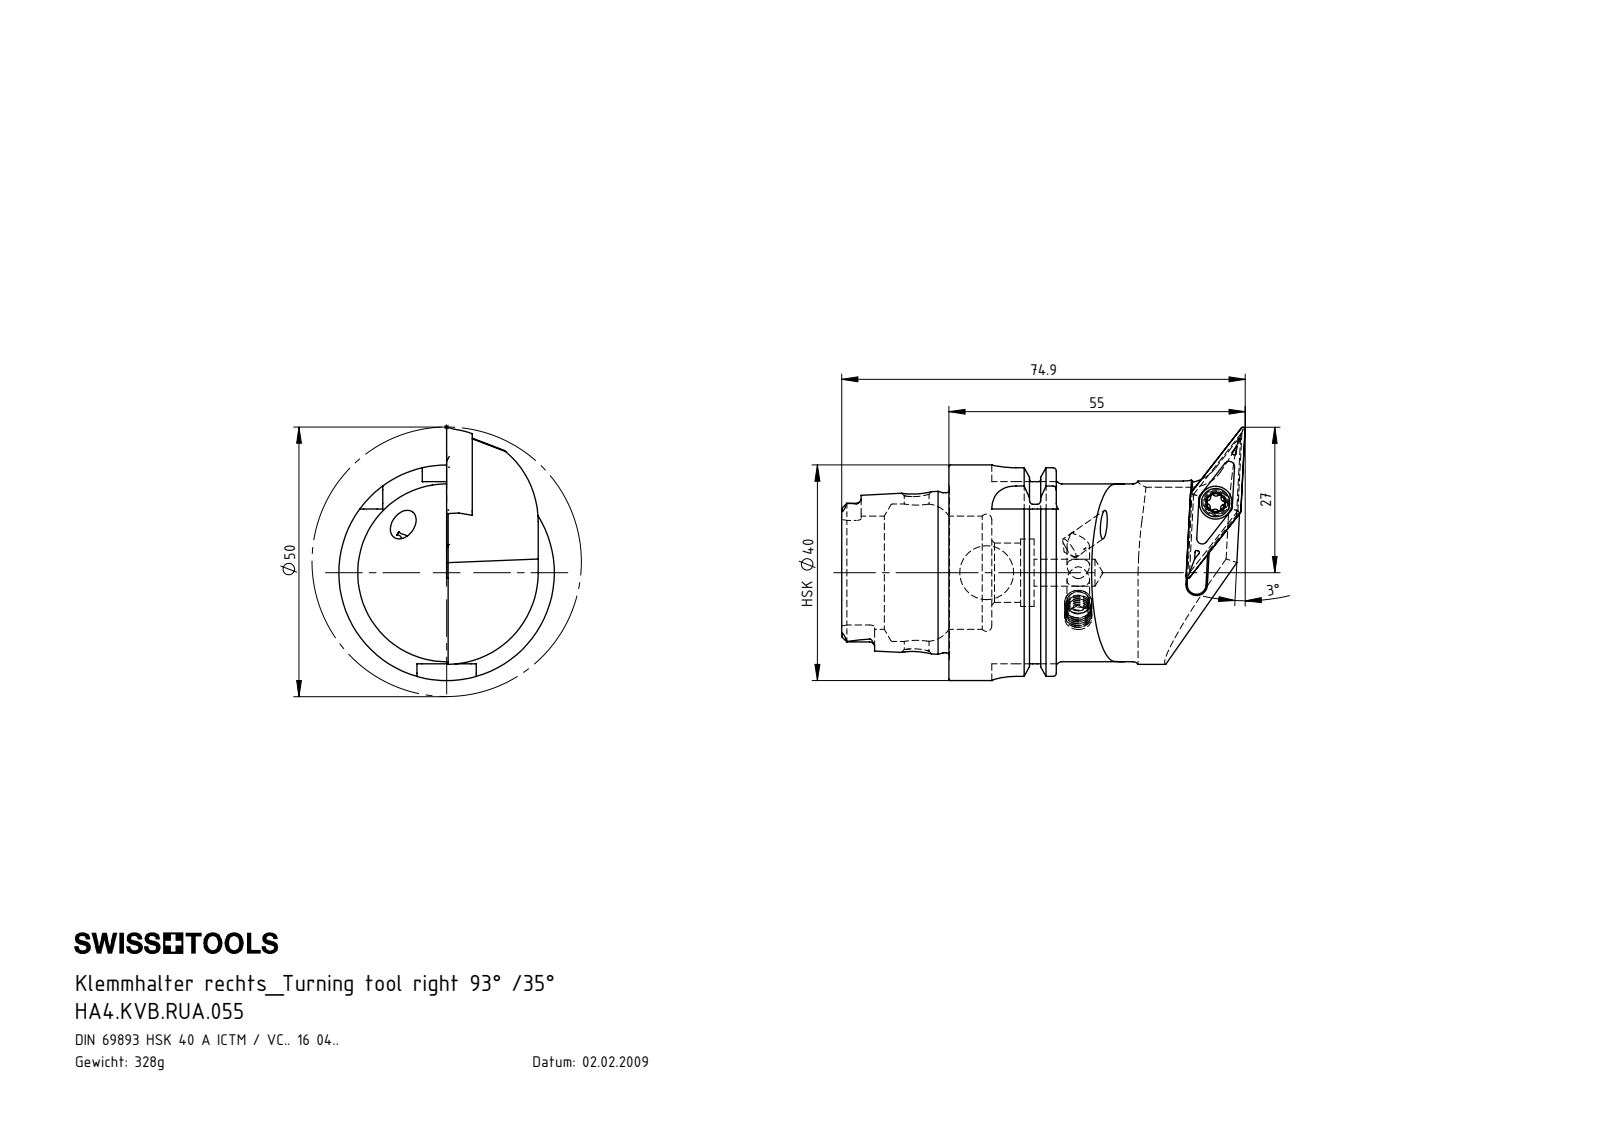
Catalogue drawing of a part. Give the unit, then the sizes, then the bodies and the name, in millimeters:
Units: millimetres
Overall size (bounding box): 74.9 × 47 × 40
Round holes (diameter × count): ⌀4.2 ×2, ⌀5 ×2, ⌀3.3 ×1, ⌀4 ×1, ⌀4.4 ×1, ⌀4.6 ×1, ⌀6.1 ×1, ⌀10 ×1, ⌀11 ×1, ⌀12.5 ×1, ⌀21 ×1, ⌀25.5 ×1
Round bosses / shafts (diameter × count): ⌀40 ×1, ⌀34.75 ×1, ⌀33 ×1, ⌀29.71 ×1, ⌀5.25 ×1, ⌀5 ×1, ⌀4 ×1
Partial cylindrical surfaces — rounded edges, fillets, slot ends (radius × count): R0.34 ×6, R0.59 ×6, R0.9 ×6, R4.5 ×4, R1.82 ×2, R1.88 ×2, R17 ×2, R1.75 ×1
Main face-to-face distances: 4.46, 7.95, 19.95, 12, 12.24, 16.7, 19.9, 27.85, 39.85, 35.7
Hole centre spacings: 44.47
Volume: 41 334 mm³ · Surface area: 14 117 mm²
Bodies: 5 solids, 321 faces (82 planar, 92 cylindrical, 147 other)
Part name (STEP PRODUCT): HA4.KVB.RUA.055; KVT_MB_600_050; VCMT160404; WCB-ER2.001.009_A (+1 more)
STEP written by: SolidWorks 2017 (AUTOMOTIVE_DESIGN)
